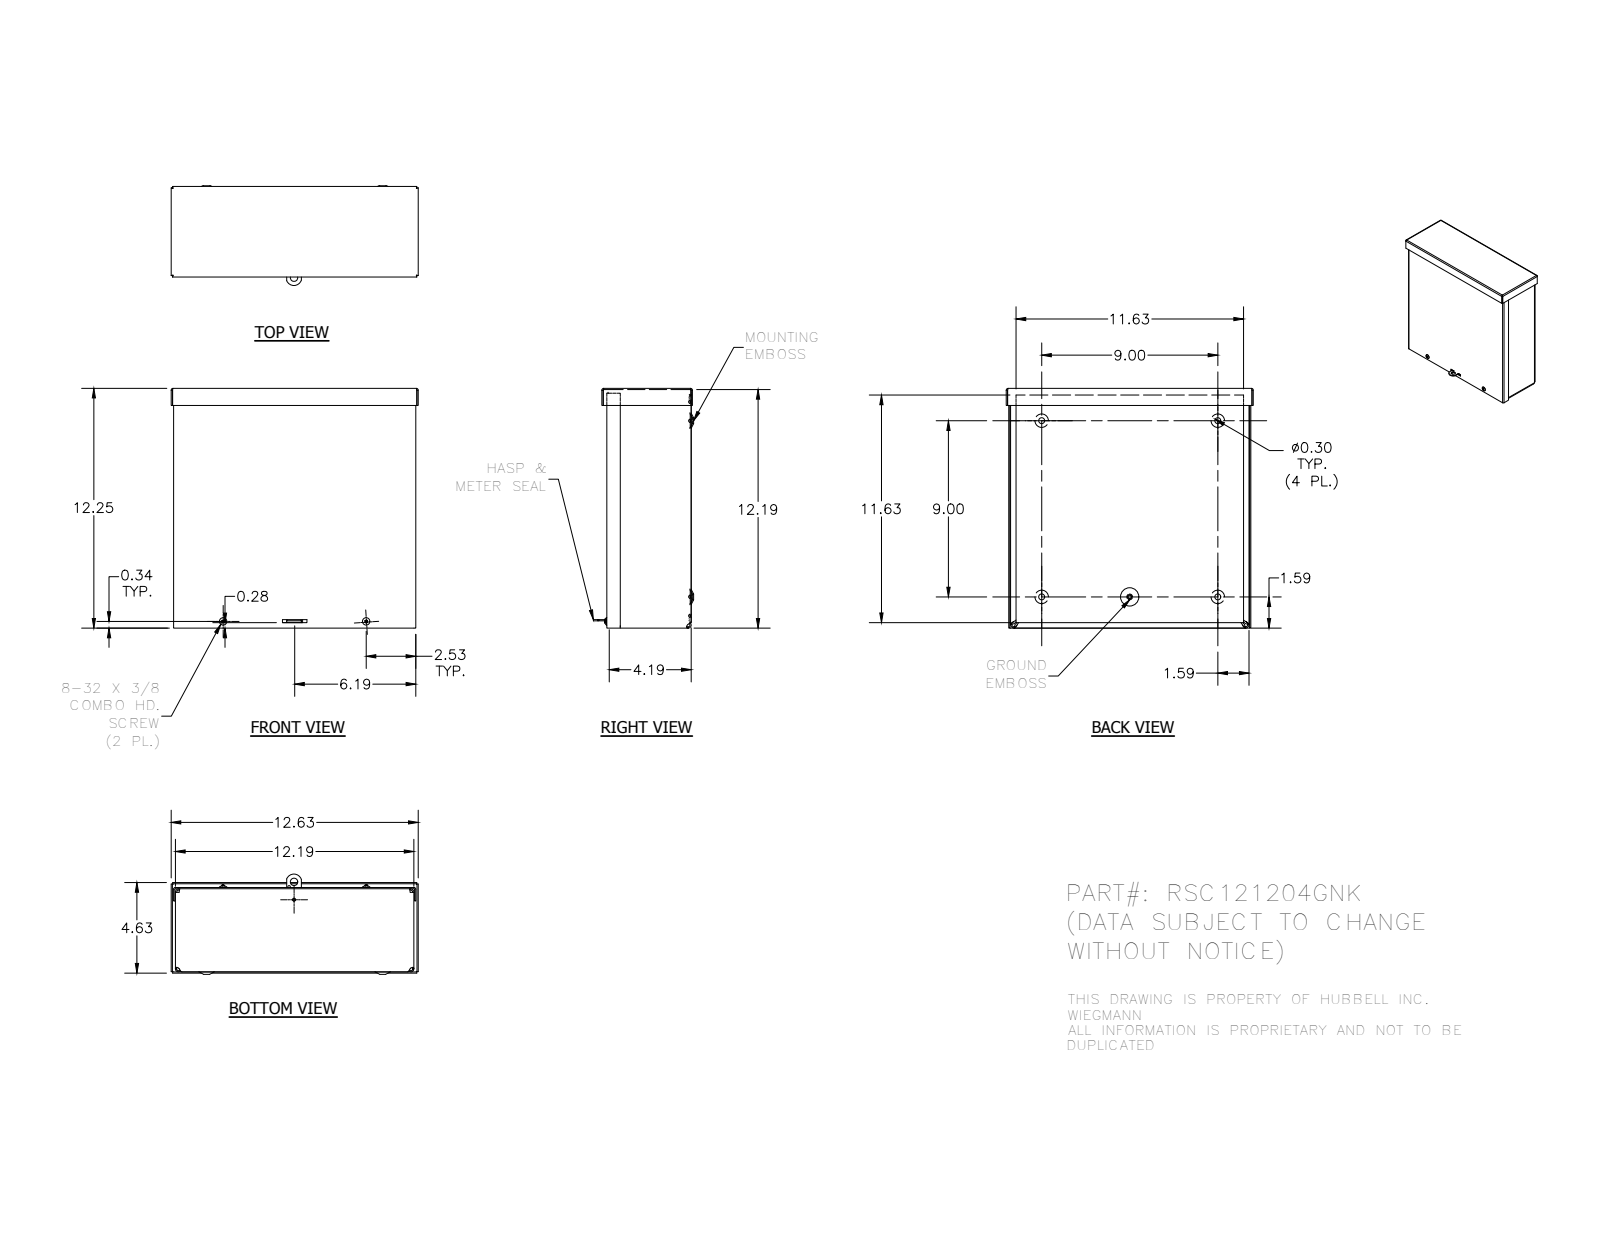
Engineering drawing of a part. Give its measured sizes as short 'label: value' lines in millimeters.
name: RSC121204GNK_WRAP; RSC1212GNK_LID; RSC1204GNK_CAP; 3183 (+3 more)
written by: Autodesk Inventor 2014 (AUTOMOTIVE_DESIGN)
unit: mm
bodies: 7 solids, 377 faces (163 planar, 78 cylindrical, 136 other)
size: 320.68 × 311.16 × 130.17
volume: 664 459 mm³; area: 853 910 mm²
holes: 4× ⌀7.62, 4× ⌀7.95, 2× ⌀3.17, 2× ⌀3.76, 1× ⌀3.96, 1× ⌀4.19, 1× ⌀9.52
bosses: 2× ⌀9.75, 2× ⌀4.17, 1× ⌀5.8
rounds: 8× R0.79, 8× R2.37, 8× R3.17, 8× R4.75, 4× R1.4, 4× R1.57, 4× R2.38, 4× R2.97
face distances: 1.58, 307.99, 107.93, 106.35, 1.57, 1.59, 109.52, 107.94, 309.57, 3.15
hole spacings: 228.6, 34.43, 114.3, 185.75, 255.57, 256.45, 261.26, 287.33
